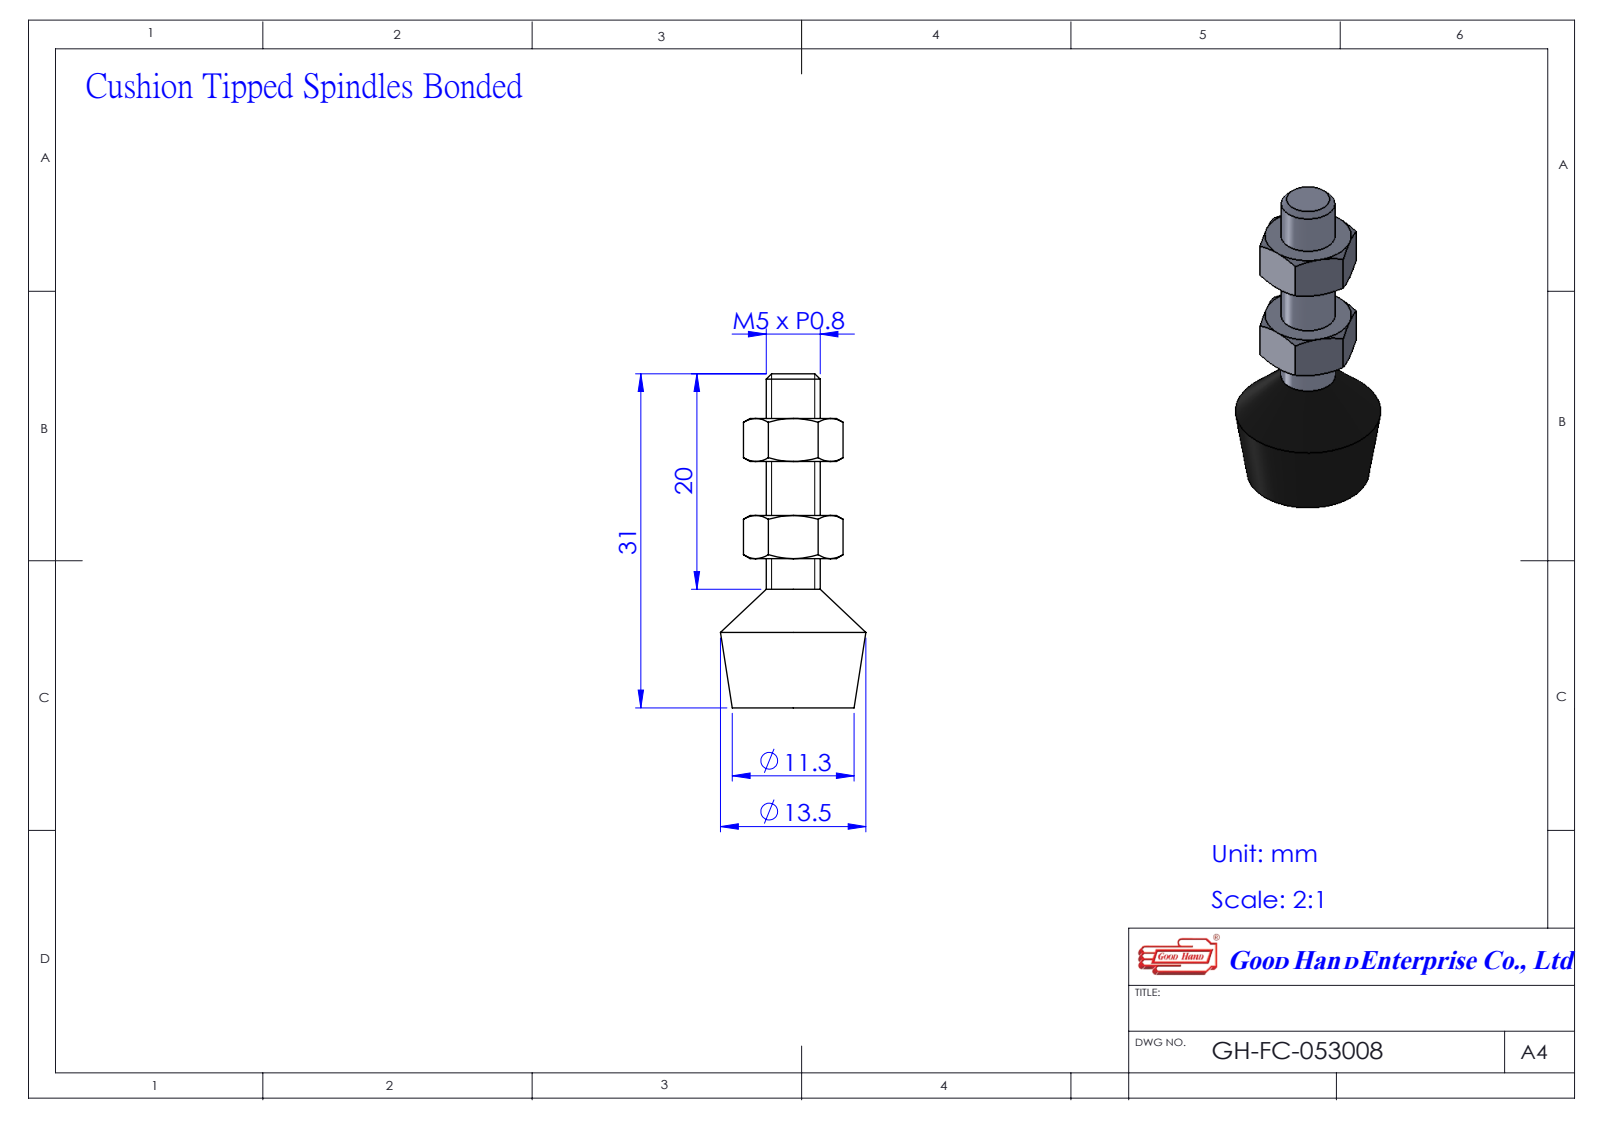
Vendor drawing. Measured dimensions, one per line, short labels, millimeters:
name: GH-FC-053008; hexagon nut_2_jis_JIS B 1181 Hexagon nut - Class 2 Finished M5 --N
written by: SolidWorks 2016 (AUTOMOTIVE_DESIGN)
unit: mm
bodies: 3 solids, 66 faces (18 planar, 10 cylindrical, 38 other)
size: 31 × 13.5 × 13.5
volume: 1 853 mm³; area: 1 348 mm²
holes: 1× ⌀4.2, 1× ⌀5
face distances: 8, 4, 9, 22.85, 13.85, 13, 26.85, 5, 17.85, 4.15
